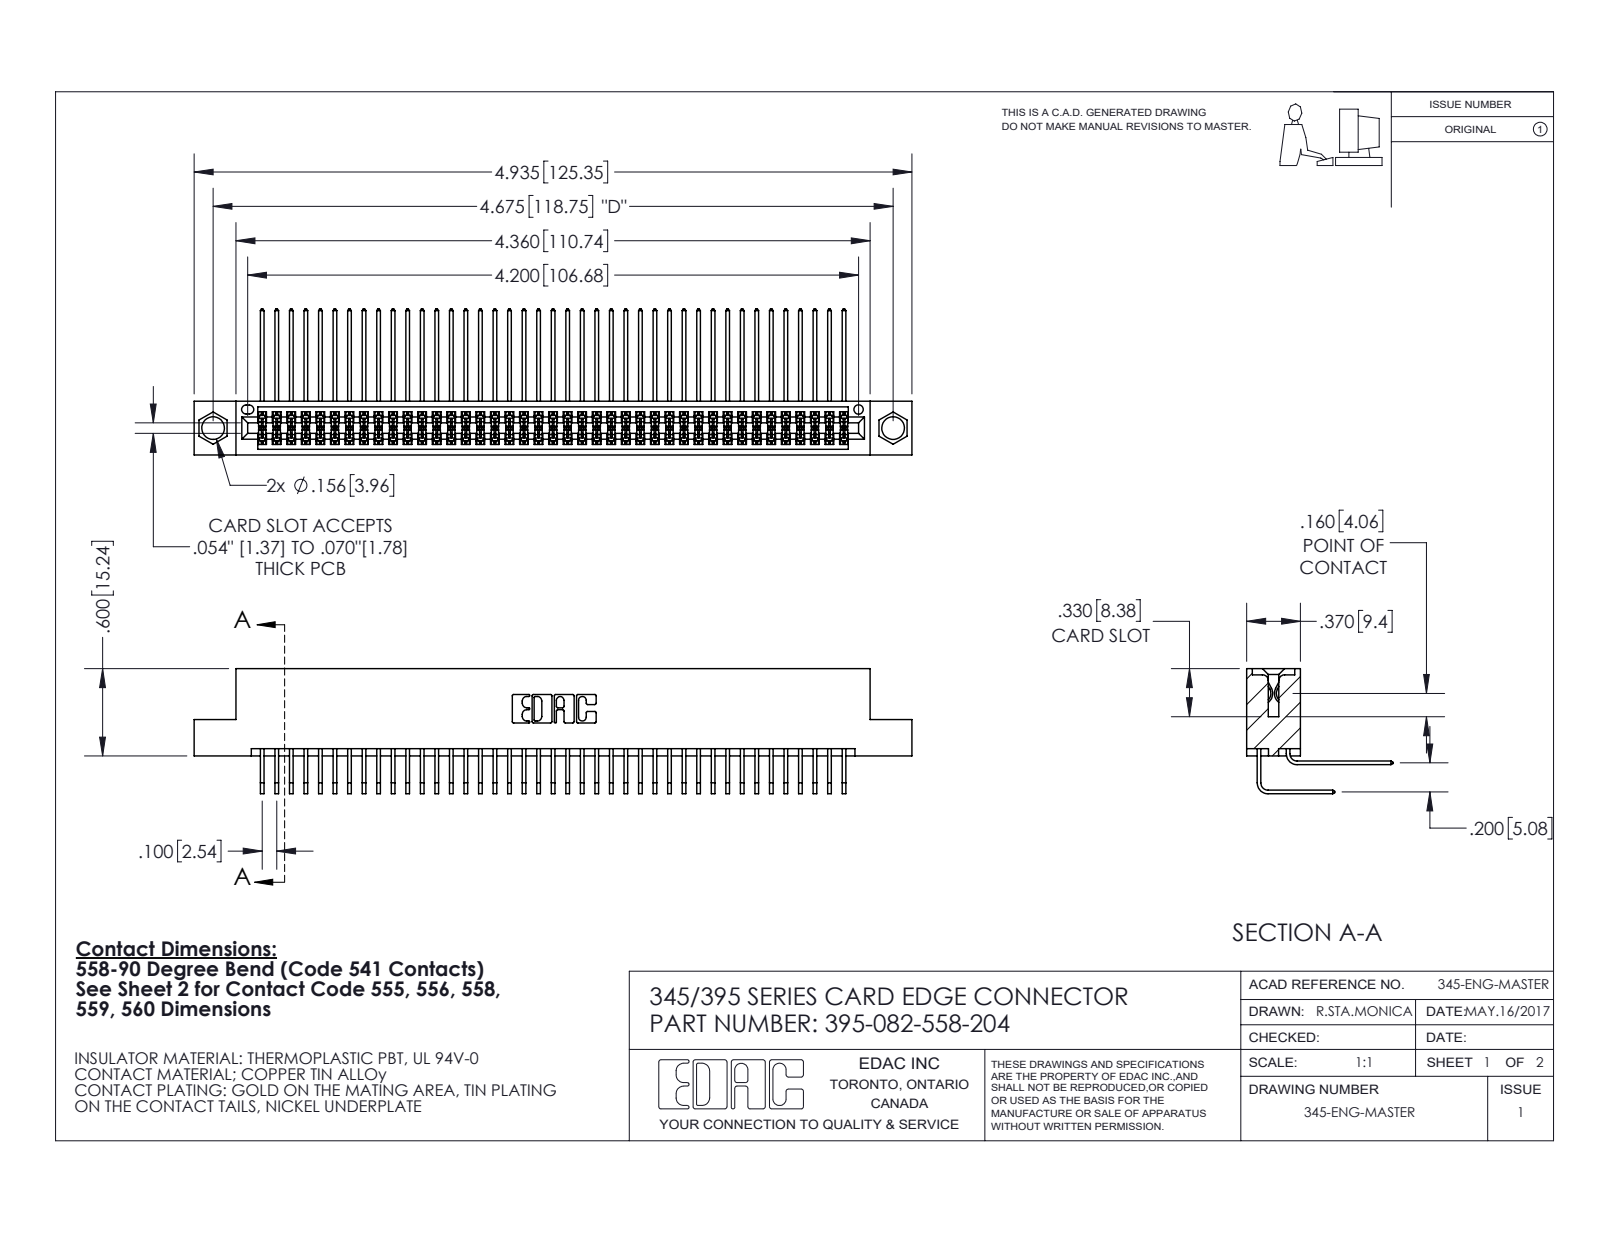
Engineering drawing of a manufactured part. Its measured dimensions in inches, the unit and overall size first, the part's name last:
Units: inches
Overall size (bounding box): 4.935 × 1.005 × 0.859
Round holes (diameter × count): ⌀0.156 ×2, ⌀0.064 ×1
Partial cylindrical surfaces — rounded edges, fillets, slot ends (radius × count): R0.006 ×123, R0.01 ×22, R0.007 ×6, R0.031 ×6, R0.026 ×3, R0.014 ×2, R0.019 ×2, R0.022 ×2
Main face-to-face distances: 0.072, 0.298, 0.2, 0.37, 0.098, 0.272, 0.025, 0.225, 0.025, 0.175
Hole centre spacings: 0.27, 4.439, 4.675
Volume: 0.765 in³ · Surface area: 31.91 in²
Bodies: 83 solids, 4404 faces (2964 planar, 1440 cylindrical, 0 other)
Part name (STEP PRODUCT): 345-292-001_558 559 Tail - 1; 345-292-001_558 Tail - 2; 345 Part_Flush Mounting Lugs - 0.156 Dia-TI; 395-082-558-204
STEP written by: SolidWorks 2020 (CONFIG_CONTROL_DESIGN)
